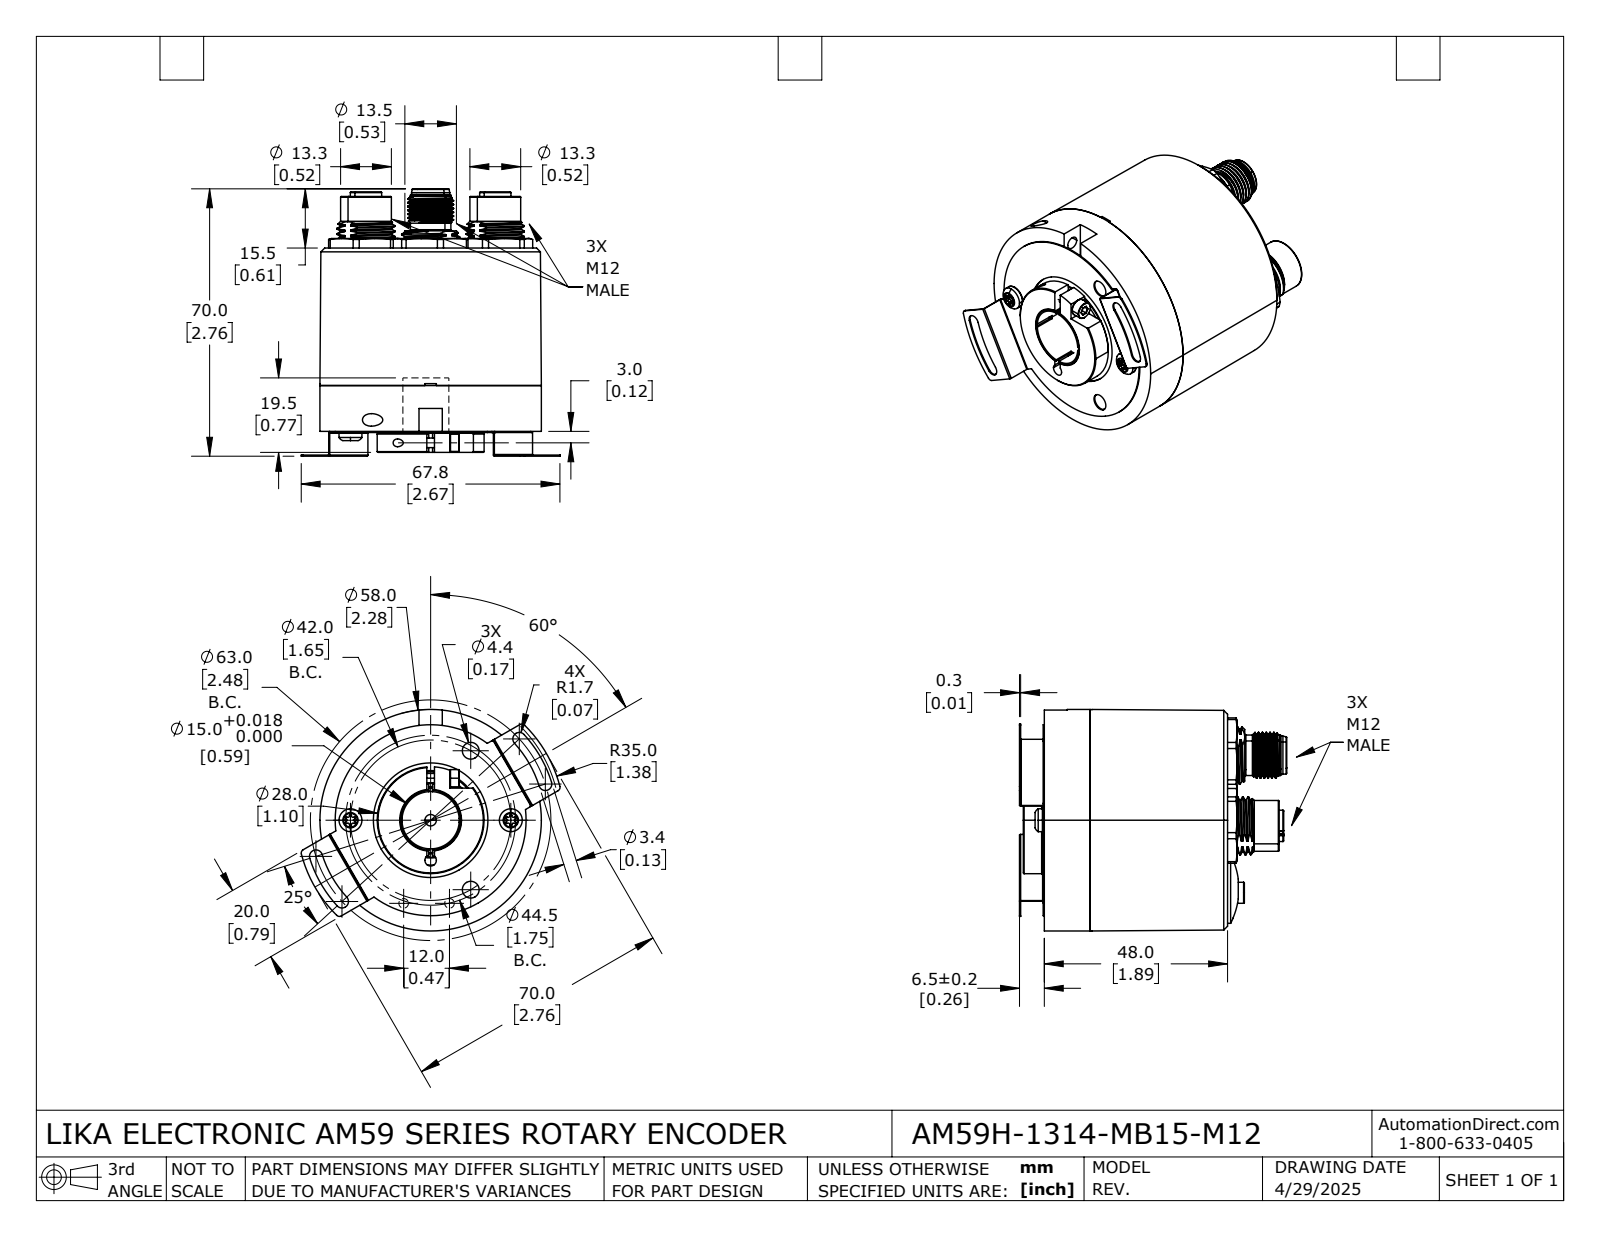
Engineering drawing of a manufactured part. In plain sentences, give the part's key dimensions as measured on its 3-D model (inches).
The part is named "AM59H-1314-MB15-M12". Its 3-D file was written by "SolidWorks 2024 (AUTOMOTIVE_DESIGN)". It is 22 solids with 1770 faces: 1028 planar, 388 cylindrical and 354 other. Overall it measures 3.125 by 2.669 by 2.531 inches. Its volume is 3.692 cubic inches and its surface area 77.91 square inches. Round holes: 7 of diameter 0.098, 5 of diameter 0.081, 4 of diameter 0.063, 2 of diameter 0.138, 2 of diameter 0.173, 2 of diameter 0.315, 1 of diameter 0.102, 1 of diameter 0.118, 1 of diameter 0.126, 1 of diameter 0.13, 1 of diameter 0.157, 1 of diameter 0.161. Round bosses or shafts: 7 of diameter 0.118, 5 of diameter 0.098, 5 of diameter 0.052, 5 of diameter 0.031, 4 of diameter 0.197, 2 of diameter 0.551, 2 of diameter 0.236, 1 of diameter 2.283. Partial cylindrical surfaces (rounded edges, fillets, slot ends): 27 of radius 0.008, 24 of radius 0.007, 24 of radius 0.015, 9 of radius 0.007, 6 of radius 0.004, 6 of radius 0.02, 4 of radius 0.006, 4 of radius 0.012. The main face-to-face distances are 2.165, 0.098, 0.118, 0.039, 0.02, 2.177, 2.079, 2.067, 0.079, 0.059. The hole center spacings are 0.827, 0.482, 0.591, 0.835, 1.27, 1.731, 0.351, 0.518.
